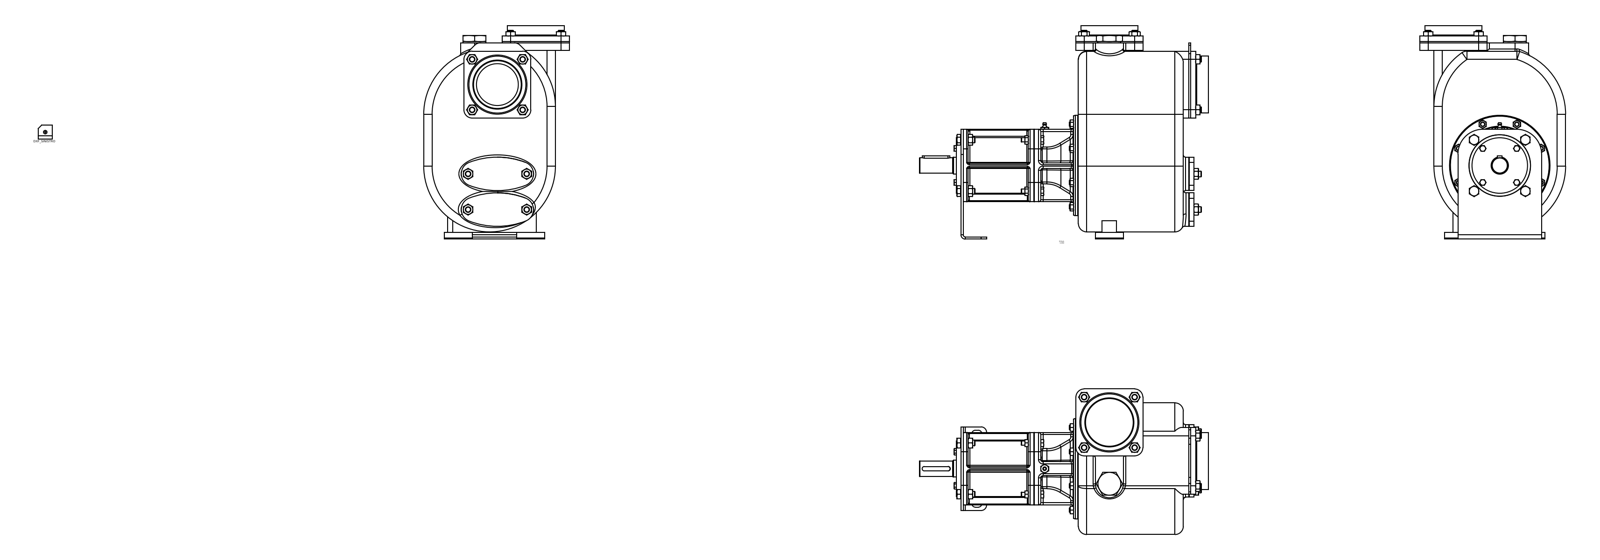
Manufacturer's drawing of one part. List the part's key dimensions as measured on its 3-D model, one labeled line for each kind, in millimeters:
Part name (STEP PRODUCT): S_82_K_B
STEP written by: CREO PARAMETRIC BY PTC INC, 2017110 (CONFIG_CONTROL_DESIGN)
Units: millimetres
Bodies: 1 solid, 828 faces (190 planar, 322 cylindrical, 316 other)
Overall size (bounding box): 517.5 × 383 × 261
Volume: 15 560 000 mm³ · Surface area: 669 910 mm²
Round holes (diameter × count): ⌀11 ×14, ⌀10 ×12, ⌀11.5 ×12, ⌀7 ×4, ⌀20 ×4, ⌀8.5 ×2, ⌀85.5 ×2, ⌀6 ×1, ⌀11.8 ×1, ⌀31 ×1, ⌀45 ×1, ⌀50 ×1
Round bosses / shafts (diameter × count): ⌀102 ×2, ⌀50 ×2, ⌀180 ×1, ⌀140 ×1, ⌀115 ×1, ⌀100 ×1, ⌀99.5 ×1, ⌀33.25 ×1
Partial cylindrical surfaces — rounded edges, fillets, slot ends (radius × count): R4 ×38, R2 ×22, R3 ×22, R15 ×19, R140 ×8, R6.5 ×4, R22 ×4, R22 ×4
Main face-to-face distances: 188, 1, 210, 6, 12, 4, 9, 15, 8, 19
Hole centre spacings: 63.99, 31.89, 43.5, 74.94, 77.94, 80, 81.51, 90.5
